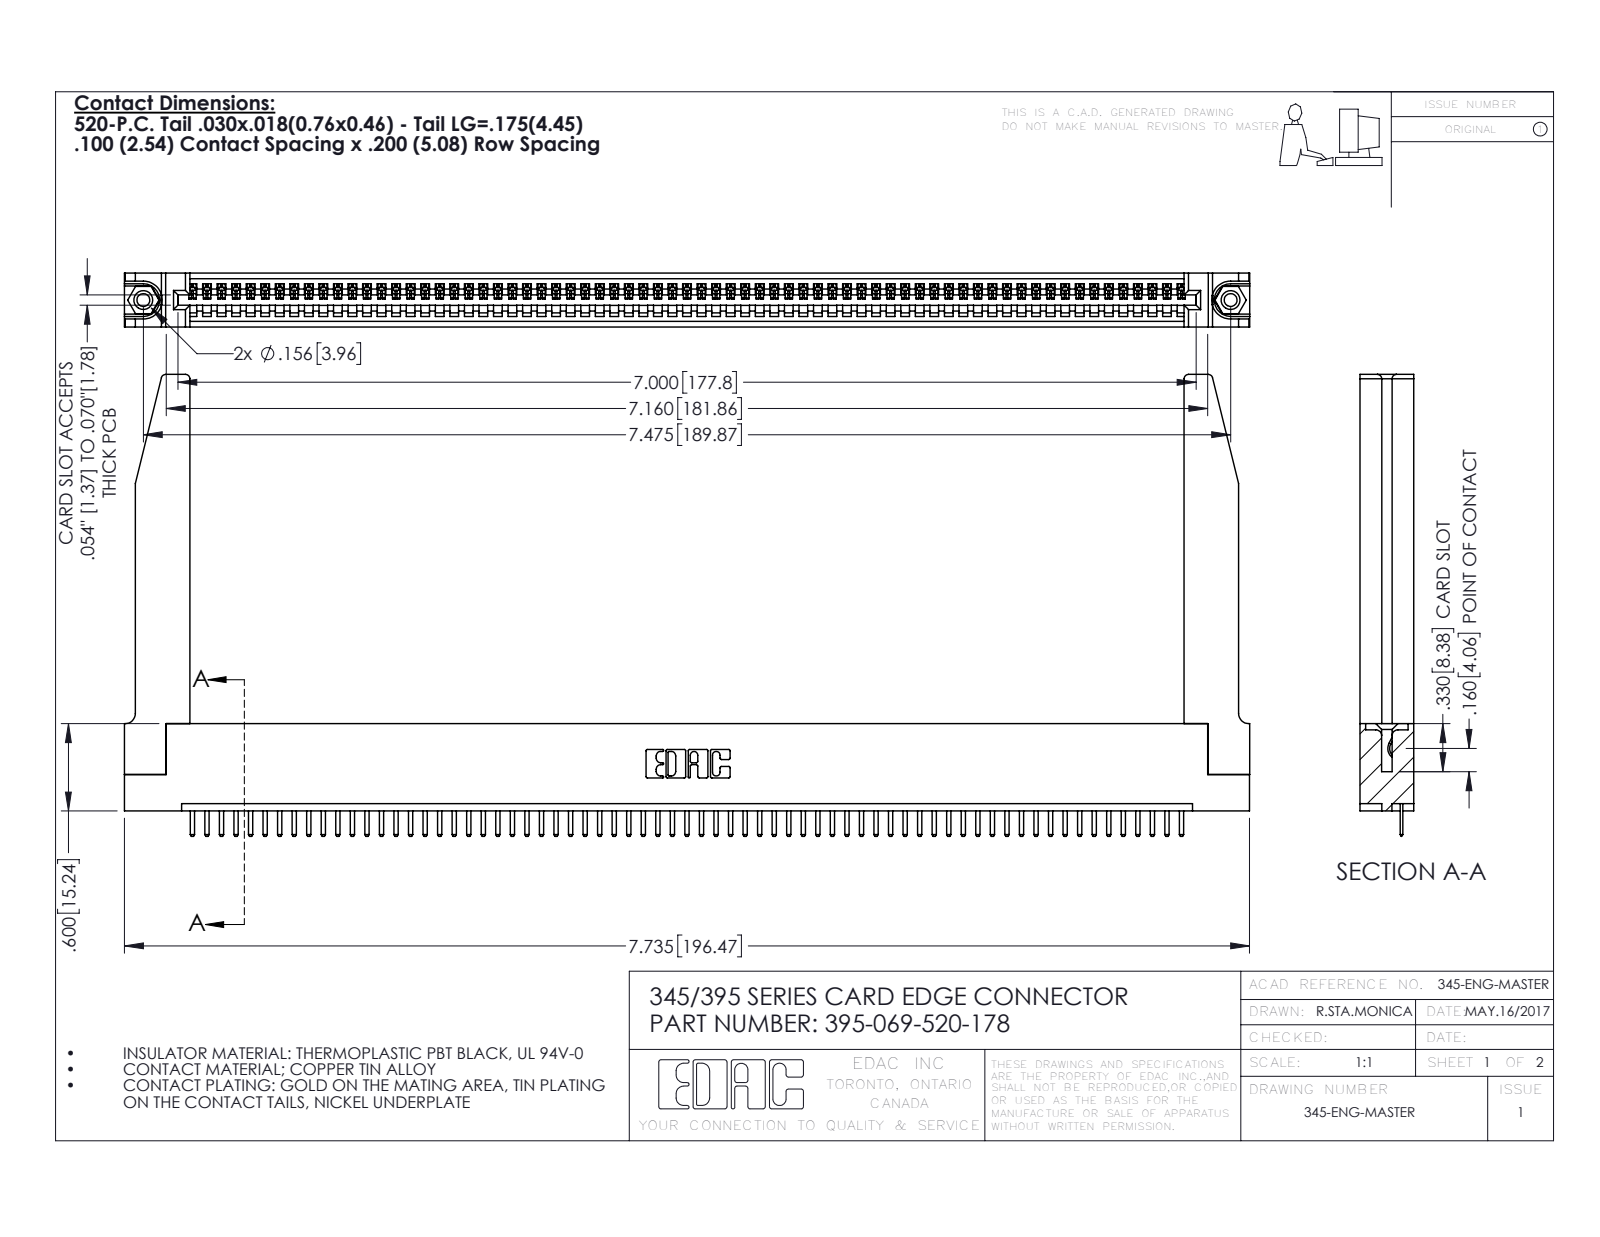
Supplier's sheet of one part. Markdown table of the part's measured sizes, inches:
| quantity | value |
| --- | --- |
| part name | 345-220-078_345-220-078; 345-250-001_345-250-001-102; 345 Part_Flush Mounting Lugs - 0.156 Dia-TH; 395-069-520-178 (+1 more) |
| STEP written by | SolidWorks 2016 (CONFIG_CONTROL_DESIGN) |
| units | inches |
| bodies | 74 solids, 4638 faces (3120 planar, 1466 cylindrical, 52 other) |
| overall size | 7.736 × 3.175 × 0.37 |
| volume | 1.614 in³ |
| surface area | 48.66 in² |
| round holes (diameter × count) | 0.089 × 2, 0.125 × 2, 0.156 × 2, 0.064 × 1 |
| round bosses / shafts (diameter × count) | 0.155 × 2 |
| partial cylindrical surfaces (radius × count) | 0.01 × 140, 0.006 × 138, 0.01 × 22, 0.03 × 8, 0.007 × 6, 0.031 × 6, 0.026 × 3, 0.031 × 2 |
| main face-to-face distances | 0.37, 0.072, 0.298, 0.2, 0.098, 0.272, 0.025, 0.225, 0.072, 0.149 |
| hole center spacings | 0.27, 7.239, 7.475 |
